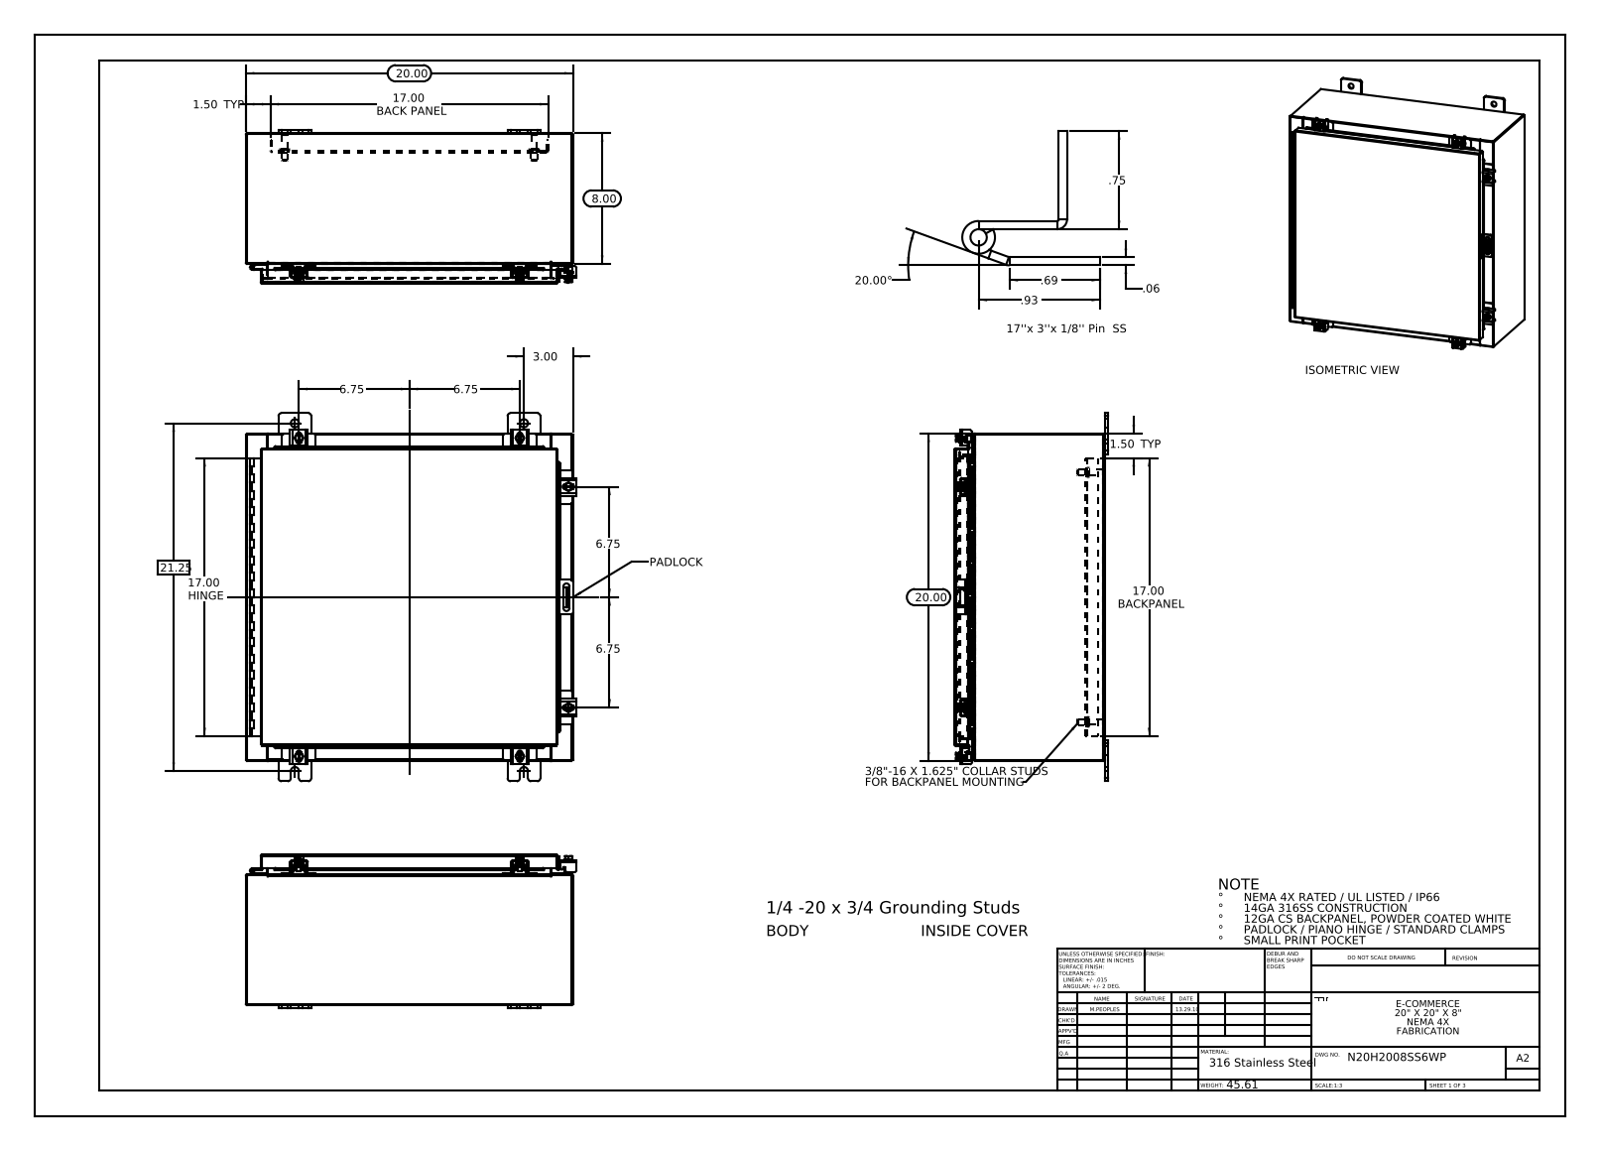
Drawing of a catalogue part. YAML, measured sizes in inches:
part_name: "N20H2008SS6WP Standard Clamps; N20H2008SS6WP Backpanel; N20H2008SS6WP Clamp Assembly; N20H2008SS6WP Clamp Top (+8 more)"
step_written_by: "SolidWorks 2013 (CONFIG_CONTROL_DESIGN)"
units: inches
bodies: {solids: 47, faces: 1613, planar: 860, cylindrical: 657, other: 96}
overall_size: [22.5, 20.211, 9.389]
volume: 160.7
surface_area: 4058
round_holes:
  - {diameter: 0.5, count: 8}
  - {diameter: 0.213, count: 6}
  - {diameter: 0.26, count: 6}
  - {diameter: 0.125, count: 2}
  - {diameter: 0.125, count: 1}
round_bosses_or_shafts:
  - {diameter: 0.25, count: 7}
  - {diameter: 0.5, count: 6}
  - {diameter: 0.399, count: 6}
  - {diameter: 0.625, count: 4}
  - {diameter: 0.375, count: 4}
  - {diameter: 0.33, count: 4}
partial_cylinders:
  - {radius: 0.06, count: 30}
  - {radius: 0.013, count: 25}
  - {radius: 0.19, count: 24}
  - {radius: 0.088, count: 21}
  - {radius: 0.12, count: 12}
  - {radius: 0.141, count: 12}
  - {radius: 0.125, count: 10}
  - {radius: 0.05, count: 9}
face_to_face_distances: [0.075, 9.126, 19.925, 9.201, 9.051, 19.85, 20, 0.104, 1, 1.075]
hole_center_spacings: [17.373, 14.528, 16.742, 22.532, 13.5, 0.431, 0.934, 1.858]
